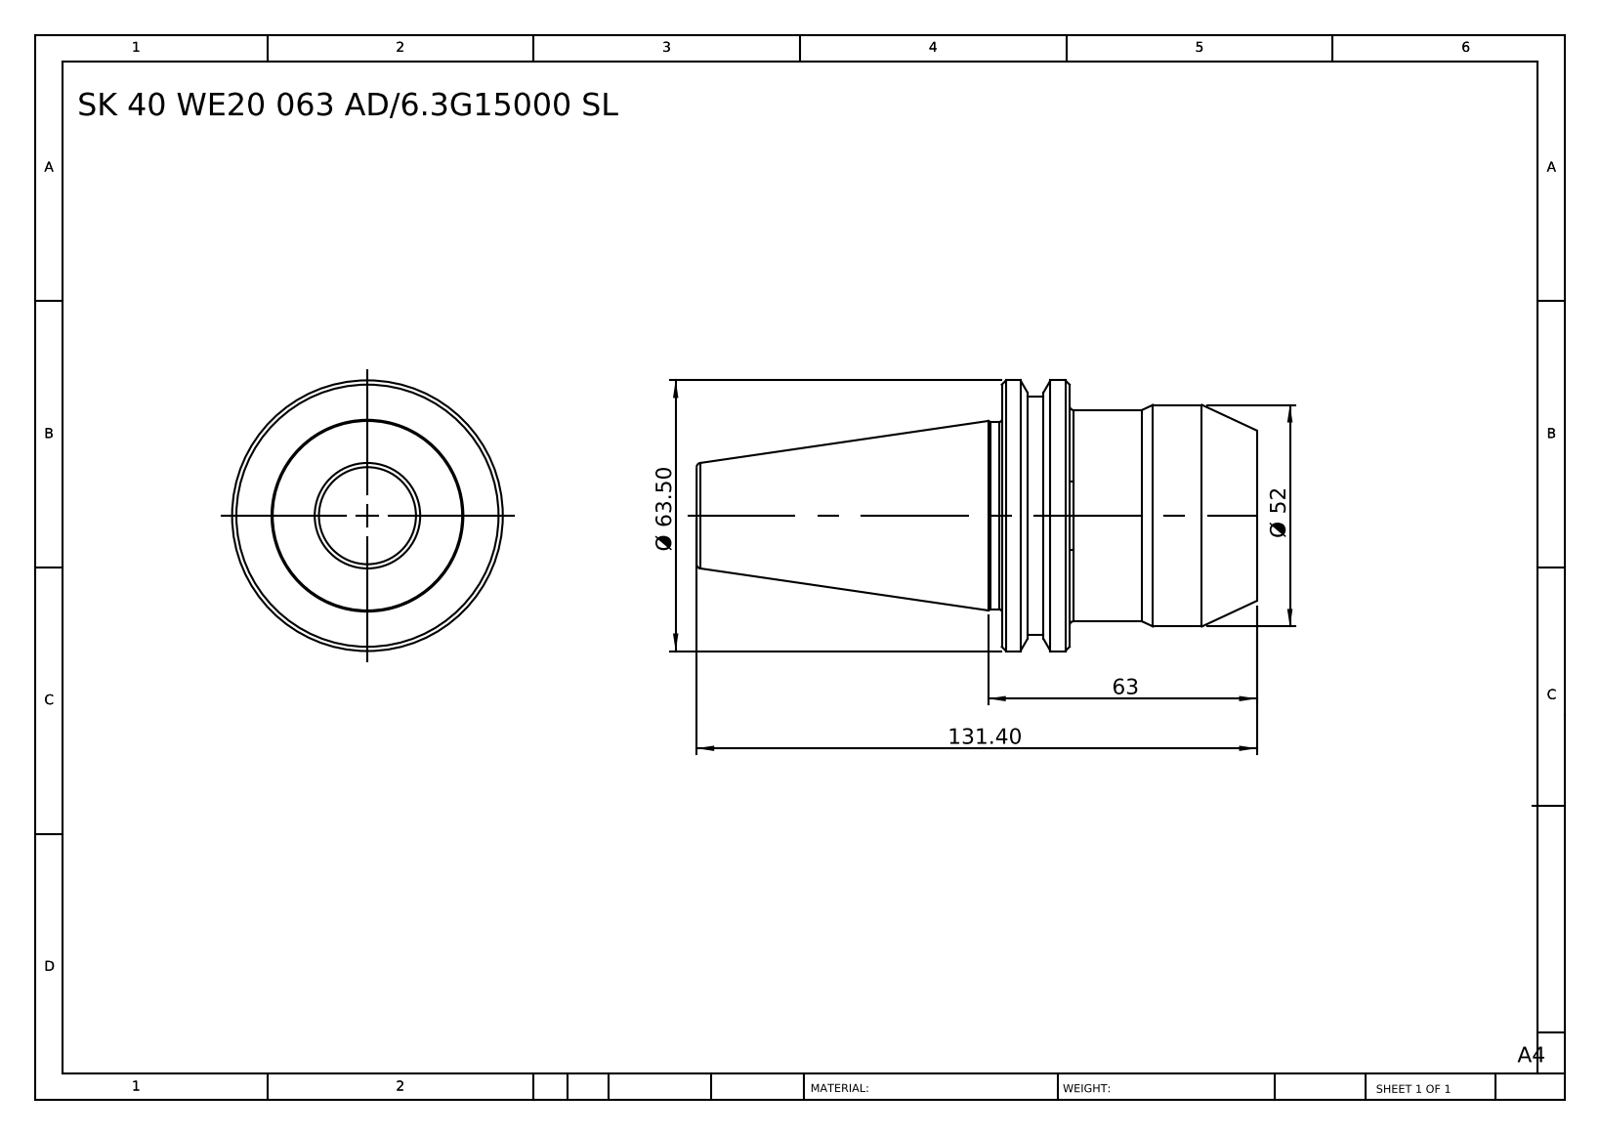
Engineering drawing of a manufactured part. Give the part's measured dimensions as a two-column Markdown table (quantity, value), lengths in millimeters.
| quantity | value |
| --- | --- |
| part name | SK40 WE20 063 AD-6.3G15000 SL |
| STEP written by | SolidWorks 2014 (CONFIG_CONTROL_DESIGN) |
| units | millimeters |
| bodies | 1 solid, 40 faces (6 planar, 12 cylindrical, 22 other) |
| overall size | 131.4 × 63.5 × 63.5 |
| volume | 200 912 mm³ |
| surface area | 23 230 mm² |
| round bosses / shafts (diameter × count) | 63.5 × 1, 56 × 1, 52 × 1, 49.5 × 1, 44 × 1 |
| main face-to-face distances | 59.8, 43.9, 15.9, 131.4, 87.5, 71.6, 50, 6.1, 9.8, 81.4 |
